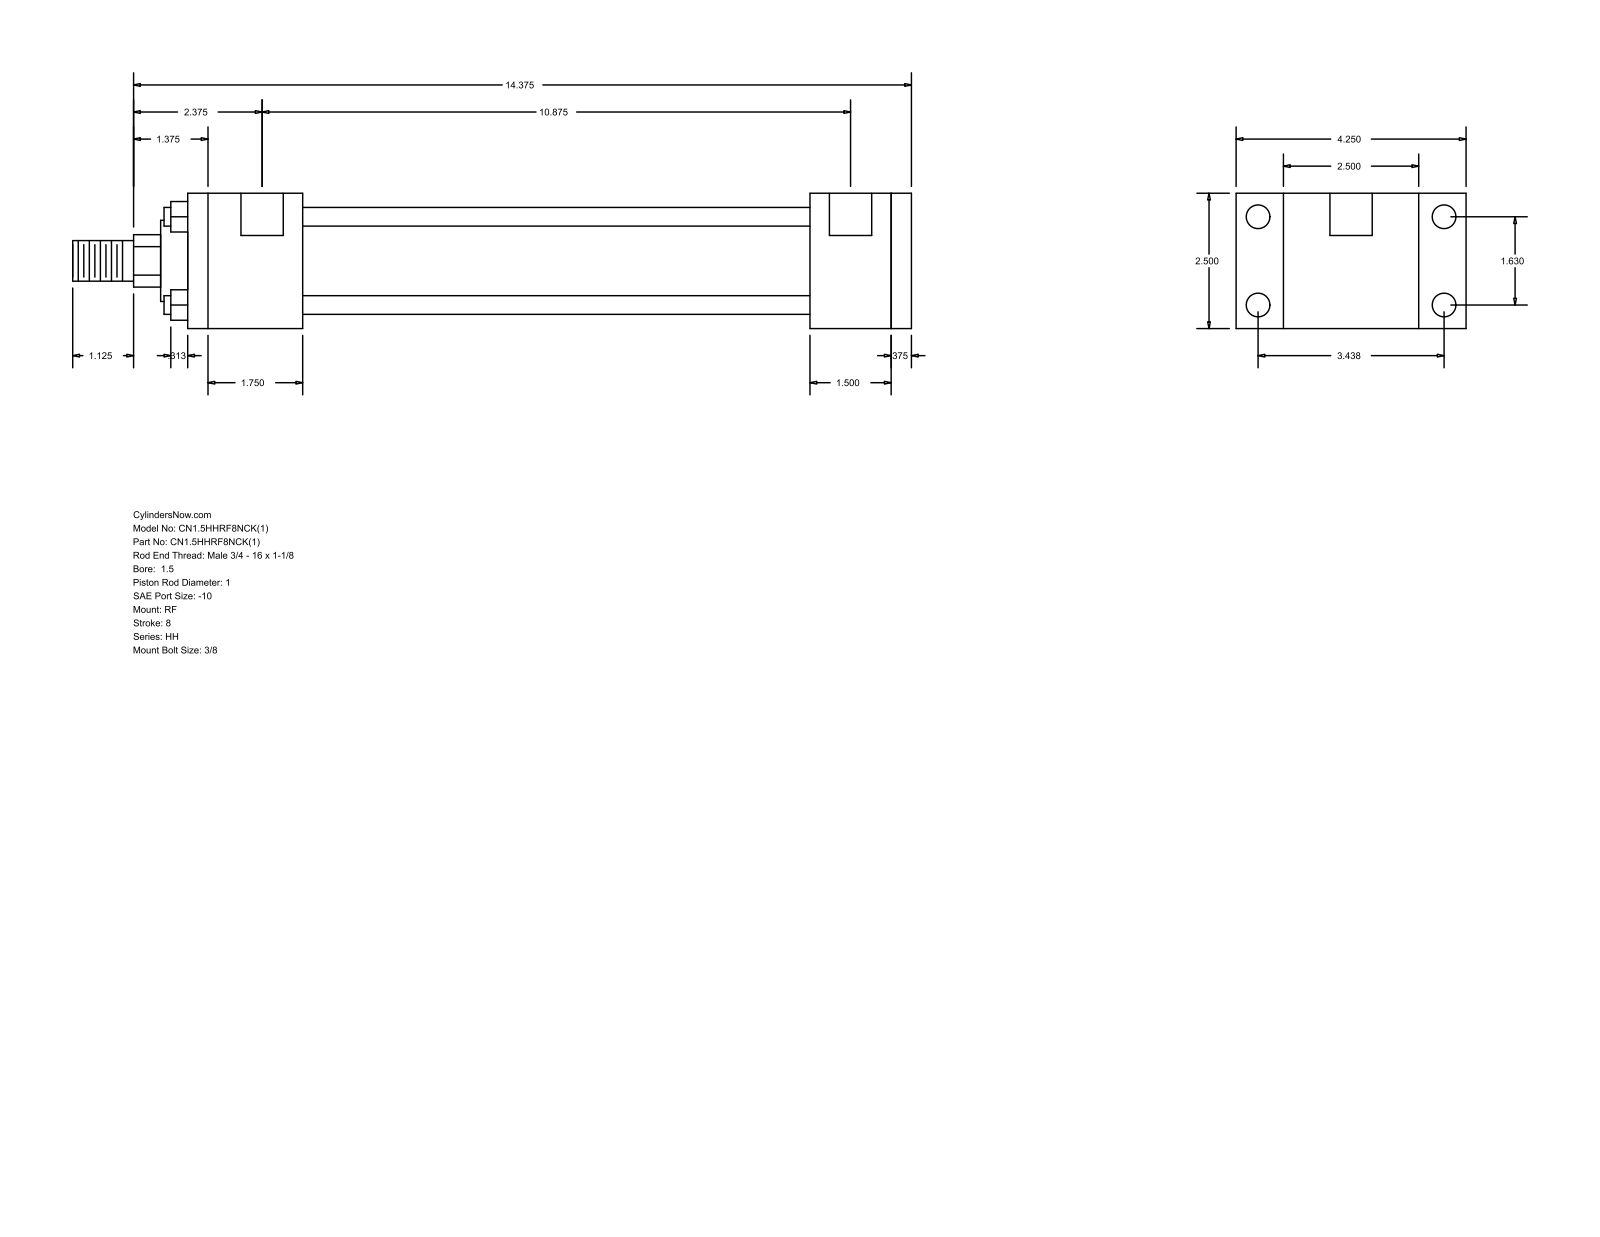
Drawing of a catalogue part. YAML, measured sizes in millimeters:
part_name: "HH_RF__0150_1"
step_written_by: "GSSL Pune (CONFIG_CONTROL_DESIGN)"
units: millimeters
bodies: {solids: 0, faces: 92, planar: 64, cylindrical: 28, other: 0}
overall_size: [393.7, 107.95, 63.5]
round_holes:
  - {diameter: 5.56, count: 4}
  - {diameter: 11.13, count: 4}
  - {diameter: 19.84, count: 2}
round_bosses_or_shafts:
  - {diameter: 8.76, count: 4}
  - {diameter: 44.45, count: 1}
  - {diameter: 38.1, count: 1}
  - {diameter: 25.4, count: 1}
  - {diameter: 19.05, count: 1}
partial_cylinders:
  - {radius: 12.29, count: 1}
face_to_face_distances: [63.5, 9.52, 38.1, 238.12, 276.22, 285.74, 47.62, 53.98, 292.1, 330.2]
hole_center_spacings: [1.59, 41.4, 87.32, 96.64, 277.81, 279.4, 276.22]
